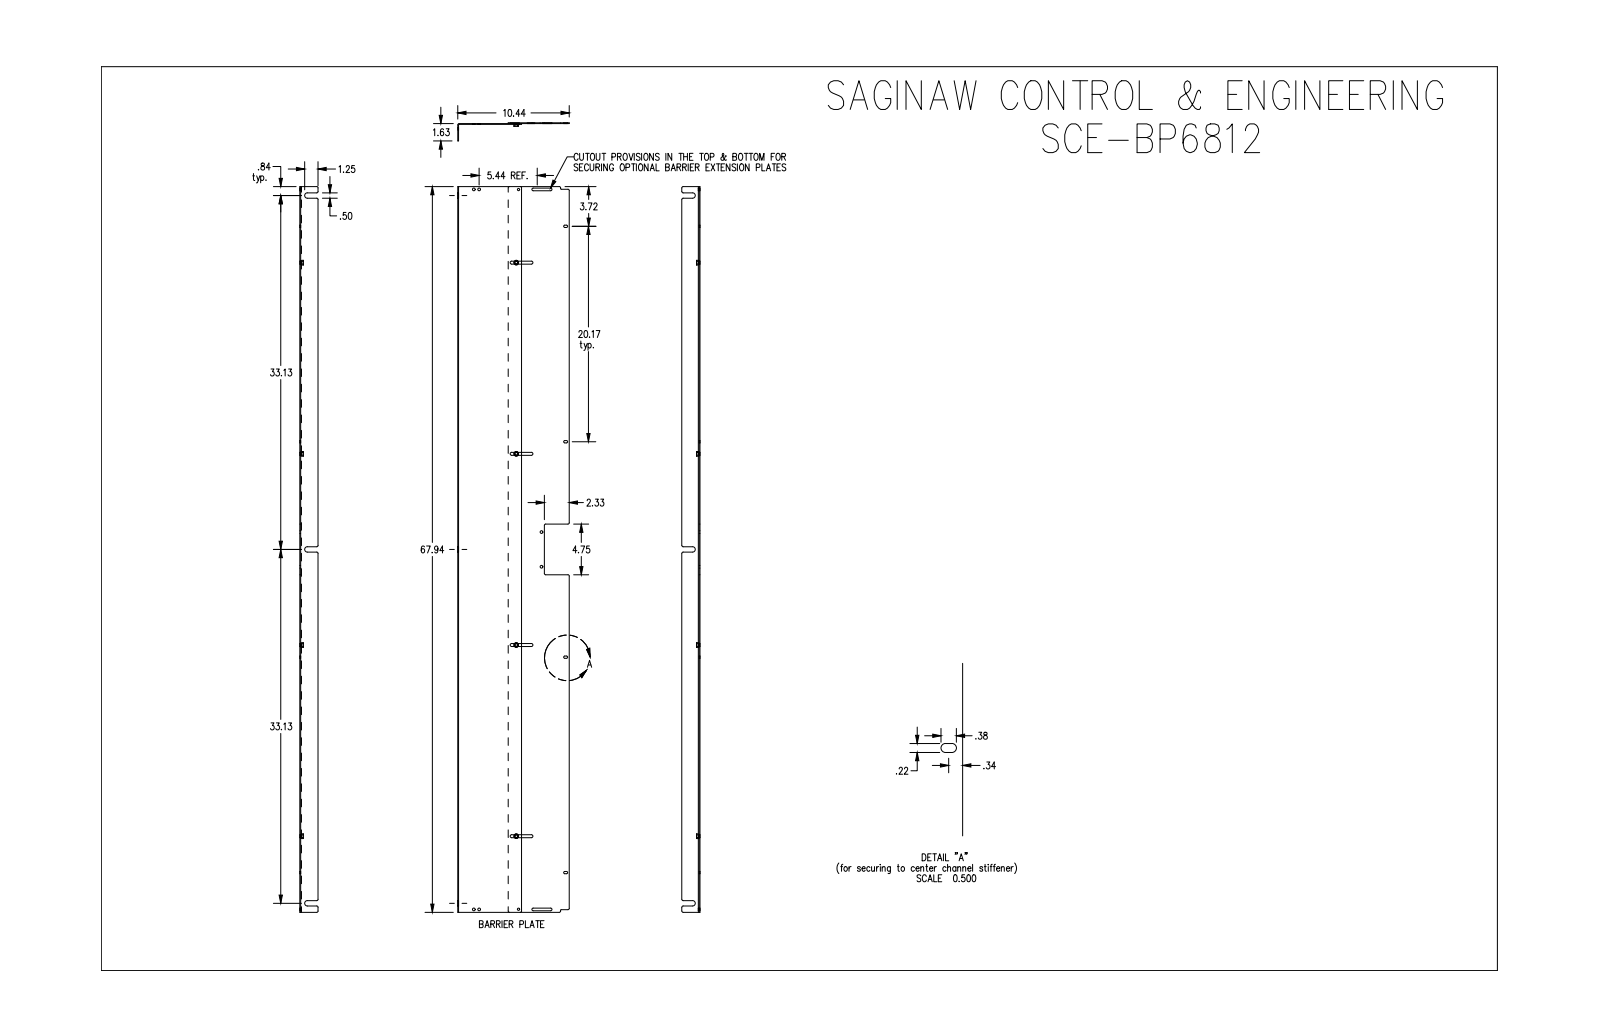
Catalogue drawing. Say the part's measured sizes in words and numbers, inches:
The part is named "SCE-BP6812". Its 3-D file was written by "SolidWorks 2019 (CONFIG_CONTROL_DESIGN)". It is 6 solids with 146 faces: 63 planar, 71 cylindrical and 12 other. Overall it measures 67.937 by 10.44 by 1.7 inches. Its volume is 66.05 cubic inches and its surface area 1 788 square inches. Round holes: 10 of diameter 0.25, 4 of diameter 0.344, 2 of diameter 0.218. Round bosses or shafts: 4 of diameter 0.44, 4 of diameter 0.343. Partial cylindrical surfaces (rounded edges, fillets, slot ends): 24 of radius 0.125, 8 of radius 0.109, 8 of radius 0.141, 3 of radius 0.25, 2 of radius 0.062, 1 of radius 0.042, 1 of radius 0.117. The main face-to-face distances are 0.075, 0.15, 4.72, 4.645, 5.97, 5.895, 1.25, 1.7, 1.625, 1.55. The hole center spacings are 0.5, 3.689, 4.189, 6.847, 7.683, 7.697, 7.922, 10.835.
